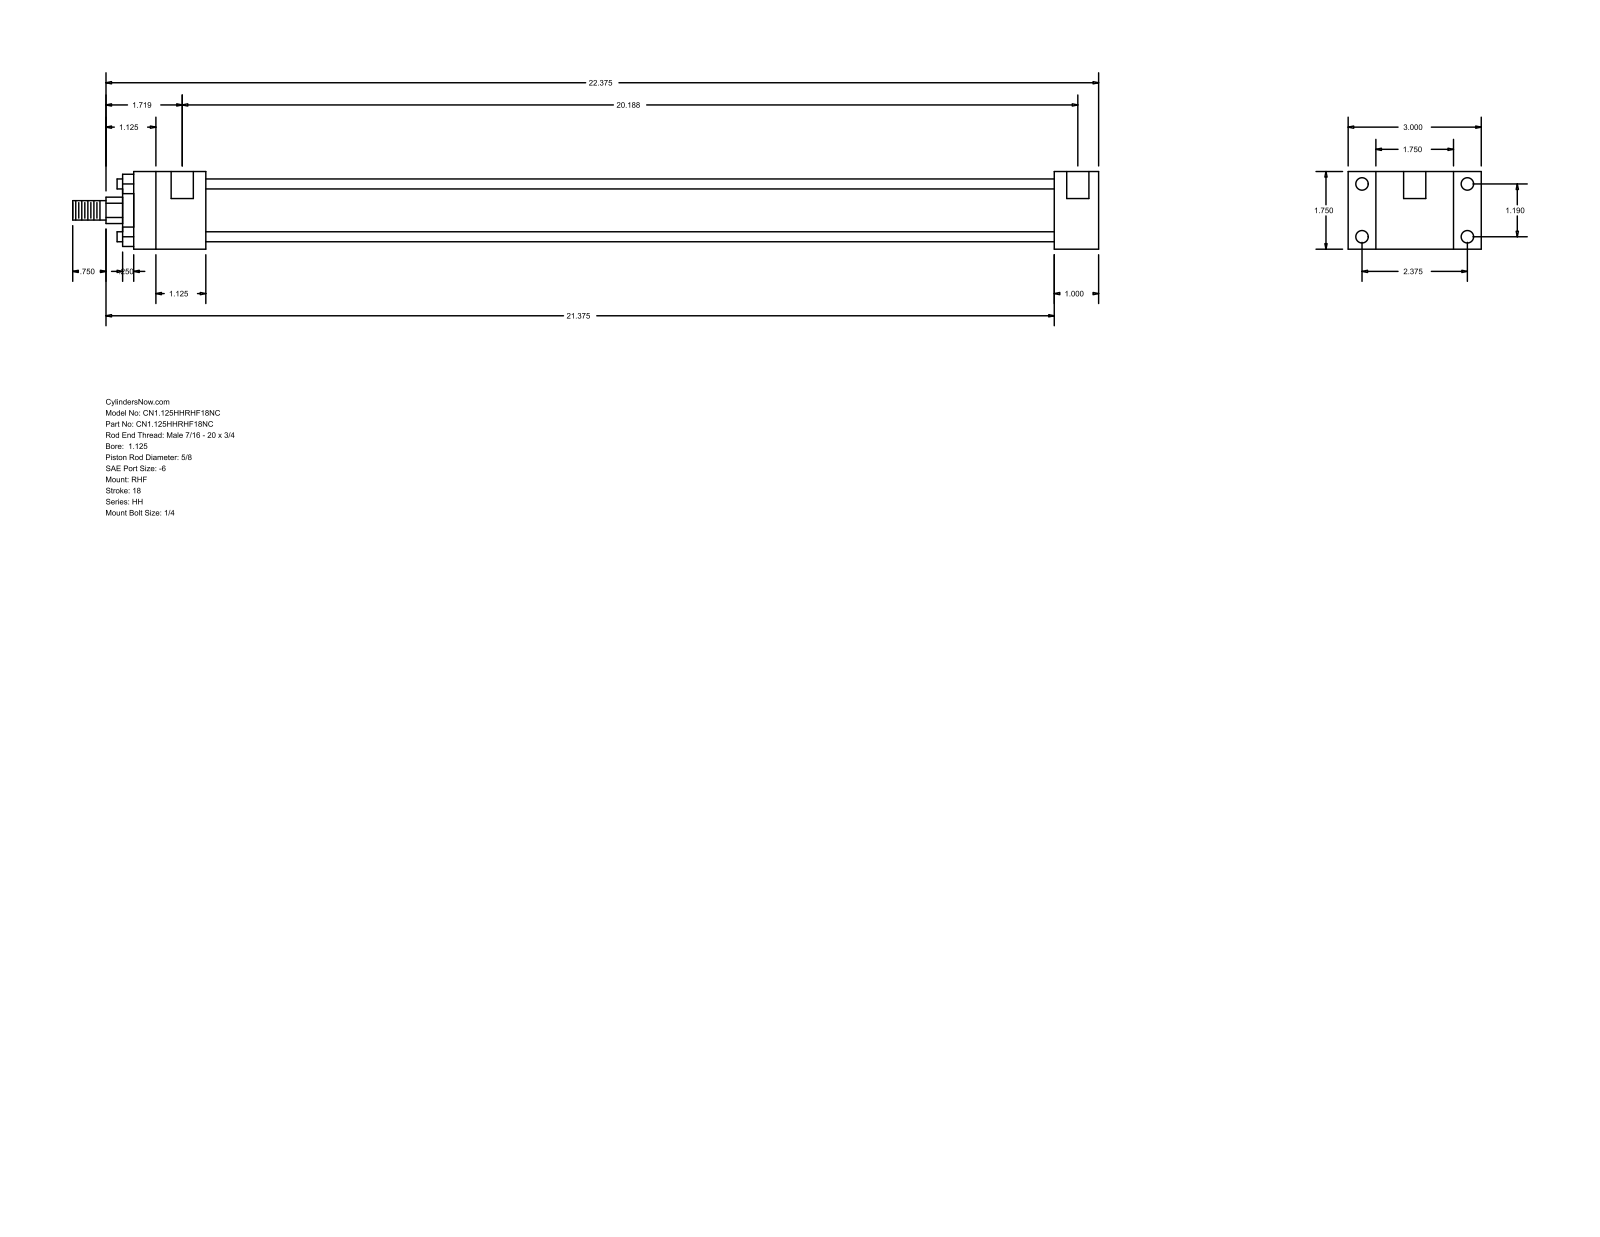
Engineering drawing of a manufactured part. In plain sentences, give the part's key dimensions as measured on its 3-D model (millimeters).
The part is named "HH_RHF__0112_0.625". Its 3-D file was written by "GSSL Pune (CONFIG_CONTROL_DESIGN)". It is 0 solids with 88 faces: 60 planar, 28 cylindrical and 0 other. Overall it measures 587.38 by 76.2 by 44.45 millimeters. Round holes: 4 of diameter 5.56, 4 of diameter 7.14, 2 of diameter 12.7. Round bosses or shafts: 4 of diameter 5.71, 1 of diameter 34.92, 1 of diameter 28.57, 1 of diameter 15.88, 1 of diameter 11.11. Partial cylindrical surfaces (rounded edges, fillets, slot ends): 1 of radius 7.54. The main face-to-face distances are 44.46, 15.87, 60.33, 25.41, 76.2, 485.77, 511.18, 41.27, 527.04, 552.45. The hole center spacings are 30.22, 60.32, 67.47, 509.59, 3.17, 512.76.
